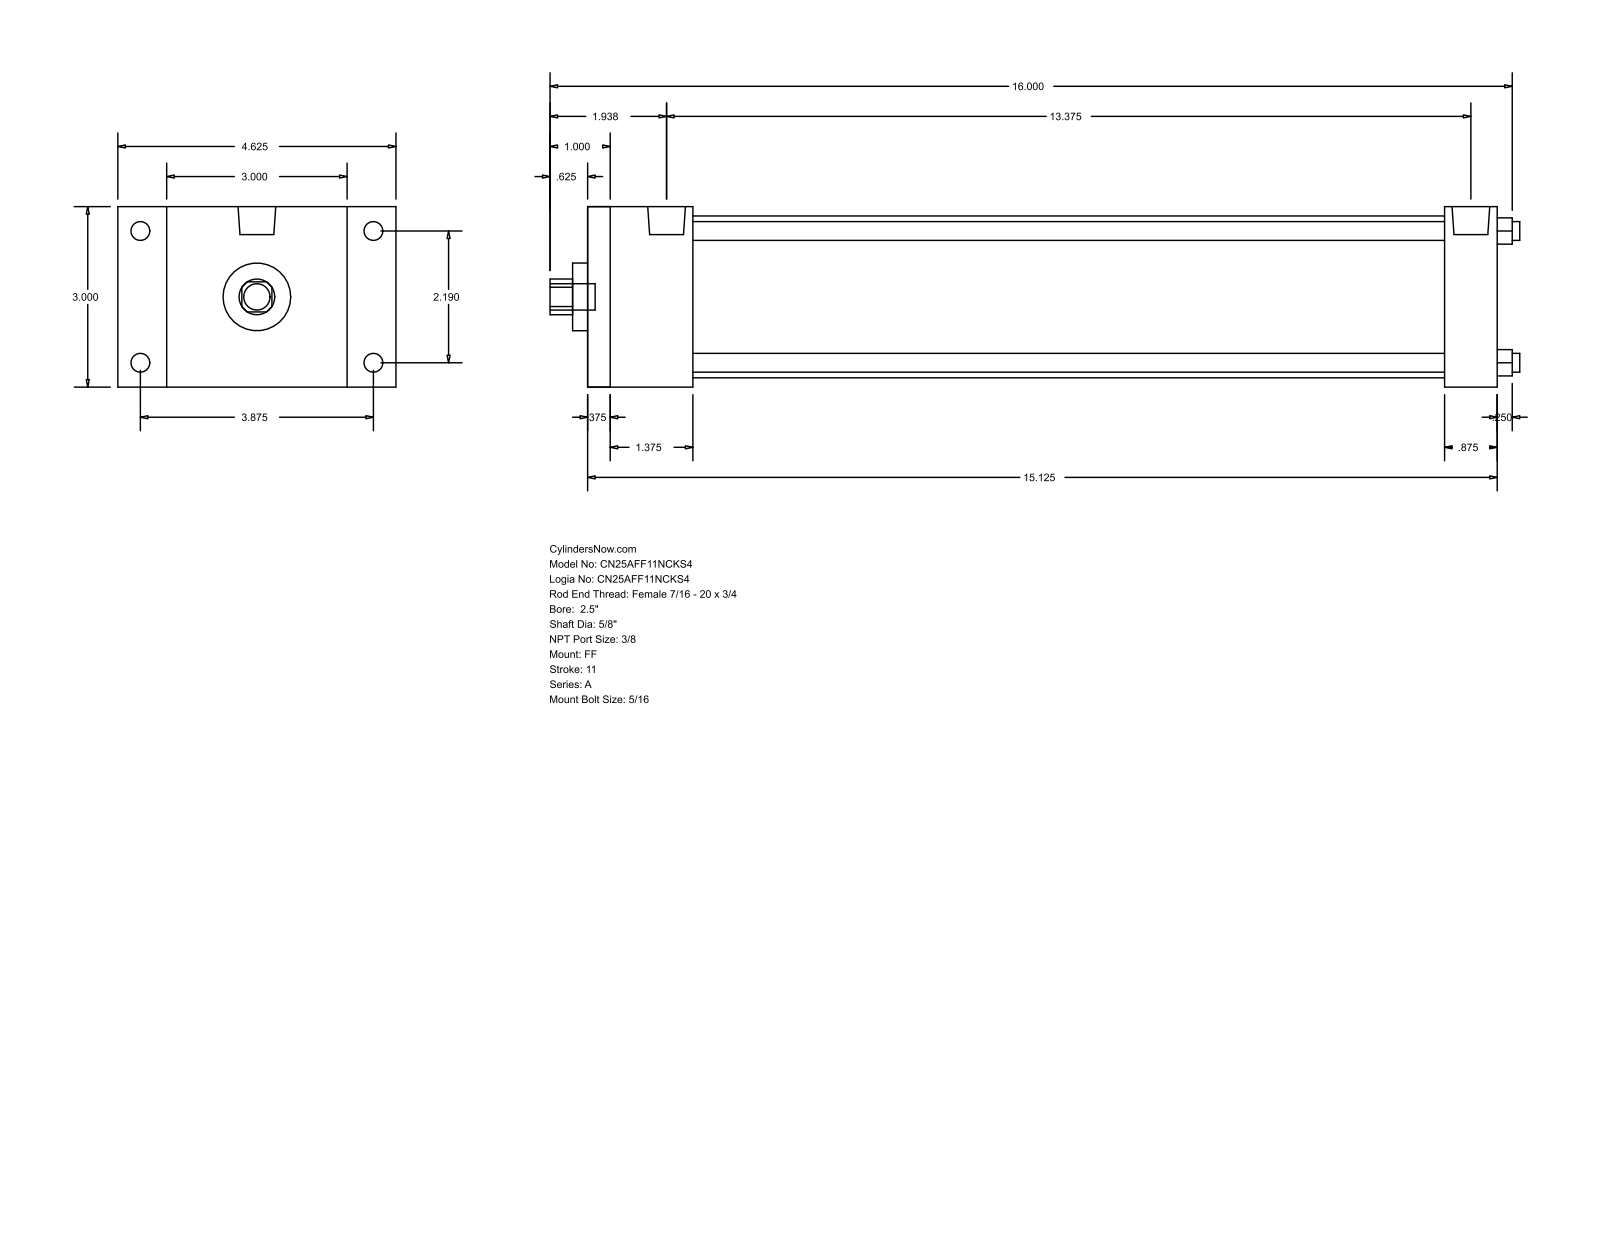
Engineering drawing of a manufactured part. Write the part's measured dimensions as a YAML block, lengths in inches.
part_name: "A_FF__0250_0.625"
step_written_by: "GSSL Pune (CONFIG_CONTROL_DESIGN)"
units: inches
bodies: {solids: 0, faces: 92, planar: 64, cylindrical: 28, other: 0}
overall_size: [16.125, 4.625, 3]
round_holes:
  - {diameter: 0.313, count: 4}
  - {diameter: 0.625, count: 1}
  - {diameter: 1.125, count: 1}
  - {diameter: 2.69, count: 1}
round_bosses_or_shafts:
  - {diameter: 0.313, count: 4}
  - {diameter: 0.219, count: 4}
  - {diameter: 0.627, count: 2}
  - {diameter: 0.437, count: 1}
partial_cylinders:
  - {radius: 0.297, count: 1}
face_to_face_distances: [3, 15.125, 0.375, 14.75, 1.75, 14.25, 1.375, 13.875, 12.5, 13.375]
hole_center_spacings: [1.548, 2.19, 3.097]
